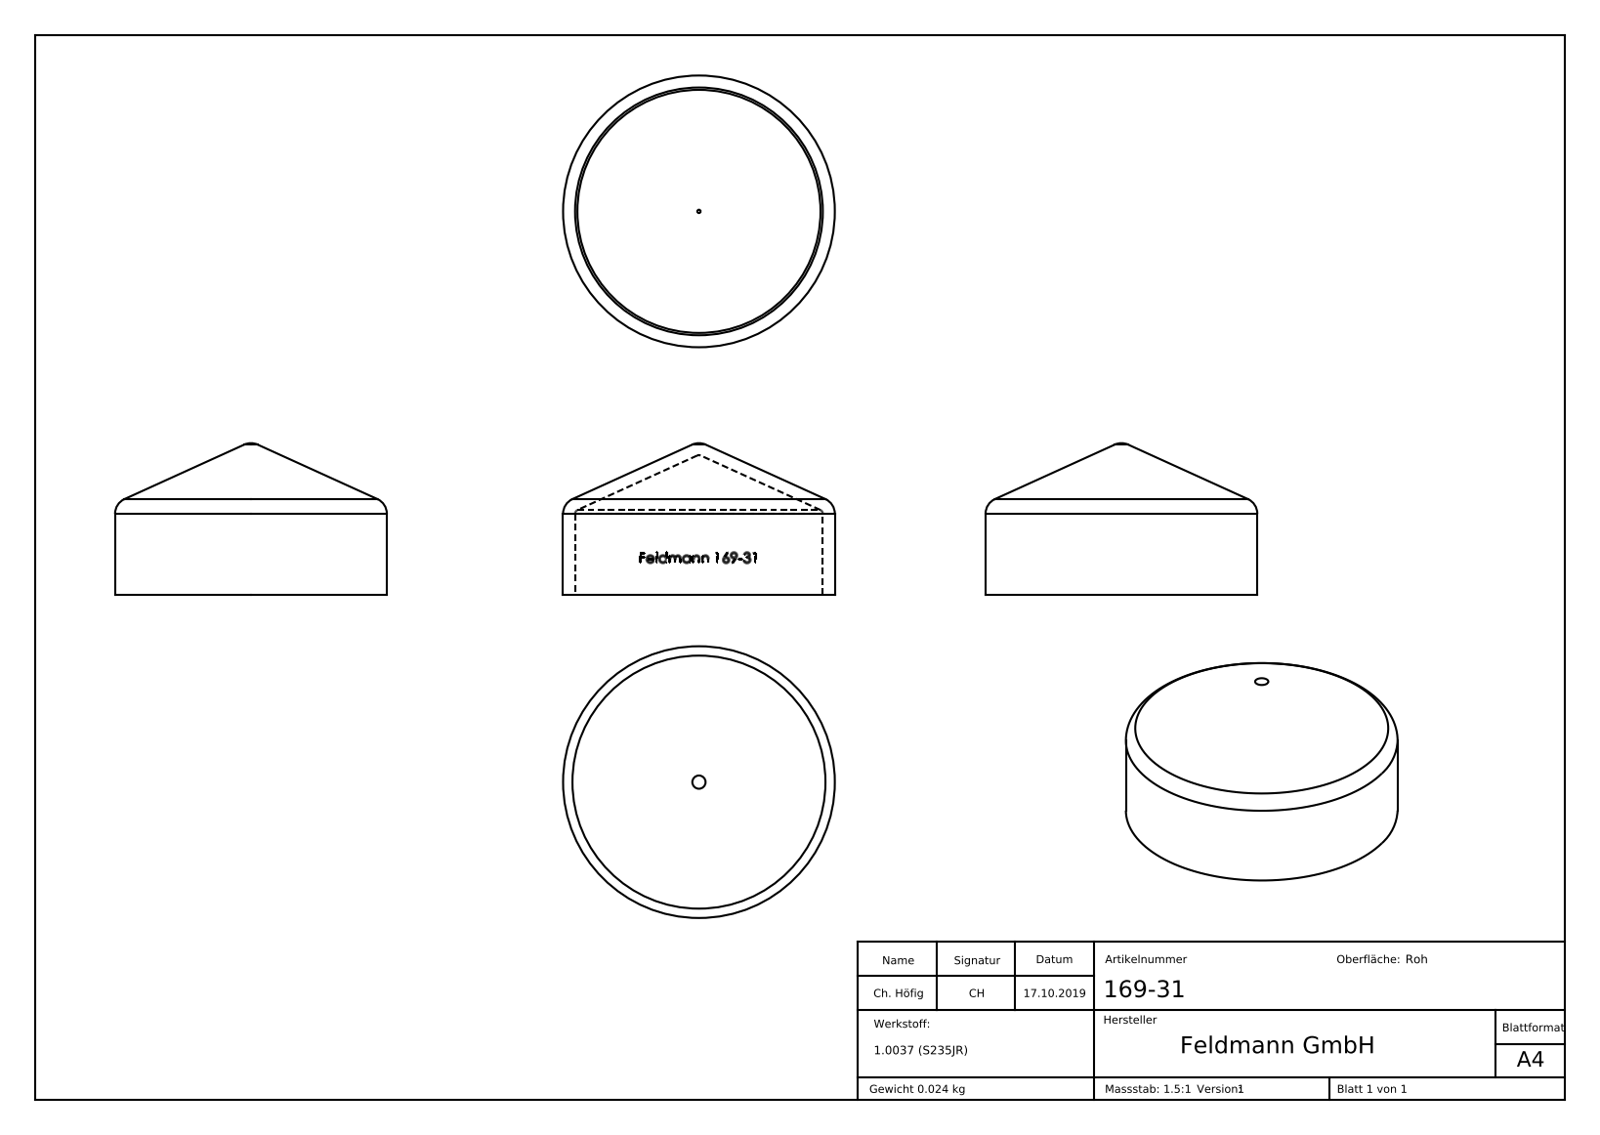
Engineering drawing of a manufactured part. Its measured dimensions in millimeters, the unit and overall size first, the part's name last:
Units: millimetres
Overall size (bounding box): 34 × 34 × 19
Round holes (diameter × count): ⌀31 ×1
Round bosses / shafts (diameter × count): ⌀34 ×1
Partial cylindrical surfaces — rounded edges, fillets, slot ends (radius × count): R15.6 ×1
Main face-to-face distances: 7.75, 2.02, 0.39, 4.68, 1.32, 1.26, 1.65, 2.97, 2.96, 3.28
Volume: 3 022 mm³ · Surface area: 4 196 mm²
Bodies: 1 solid, 187 faces (80 planar, 21 cylindrical, 86 other)
Part name (STEP PRODUCT): 169-31
STEP written by: SolidWorks 2015 (CONFIG_CONTROL_DESIGN)
